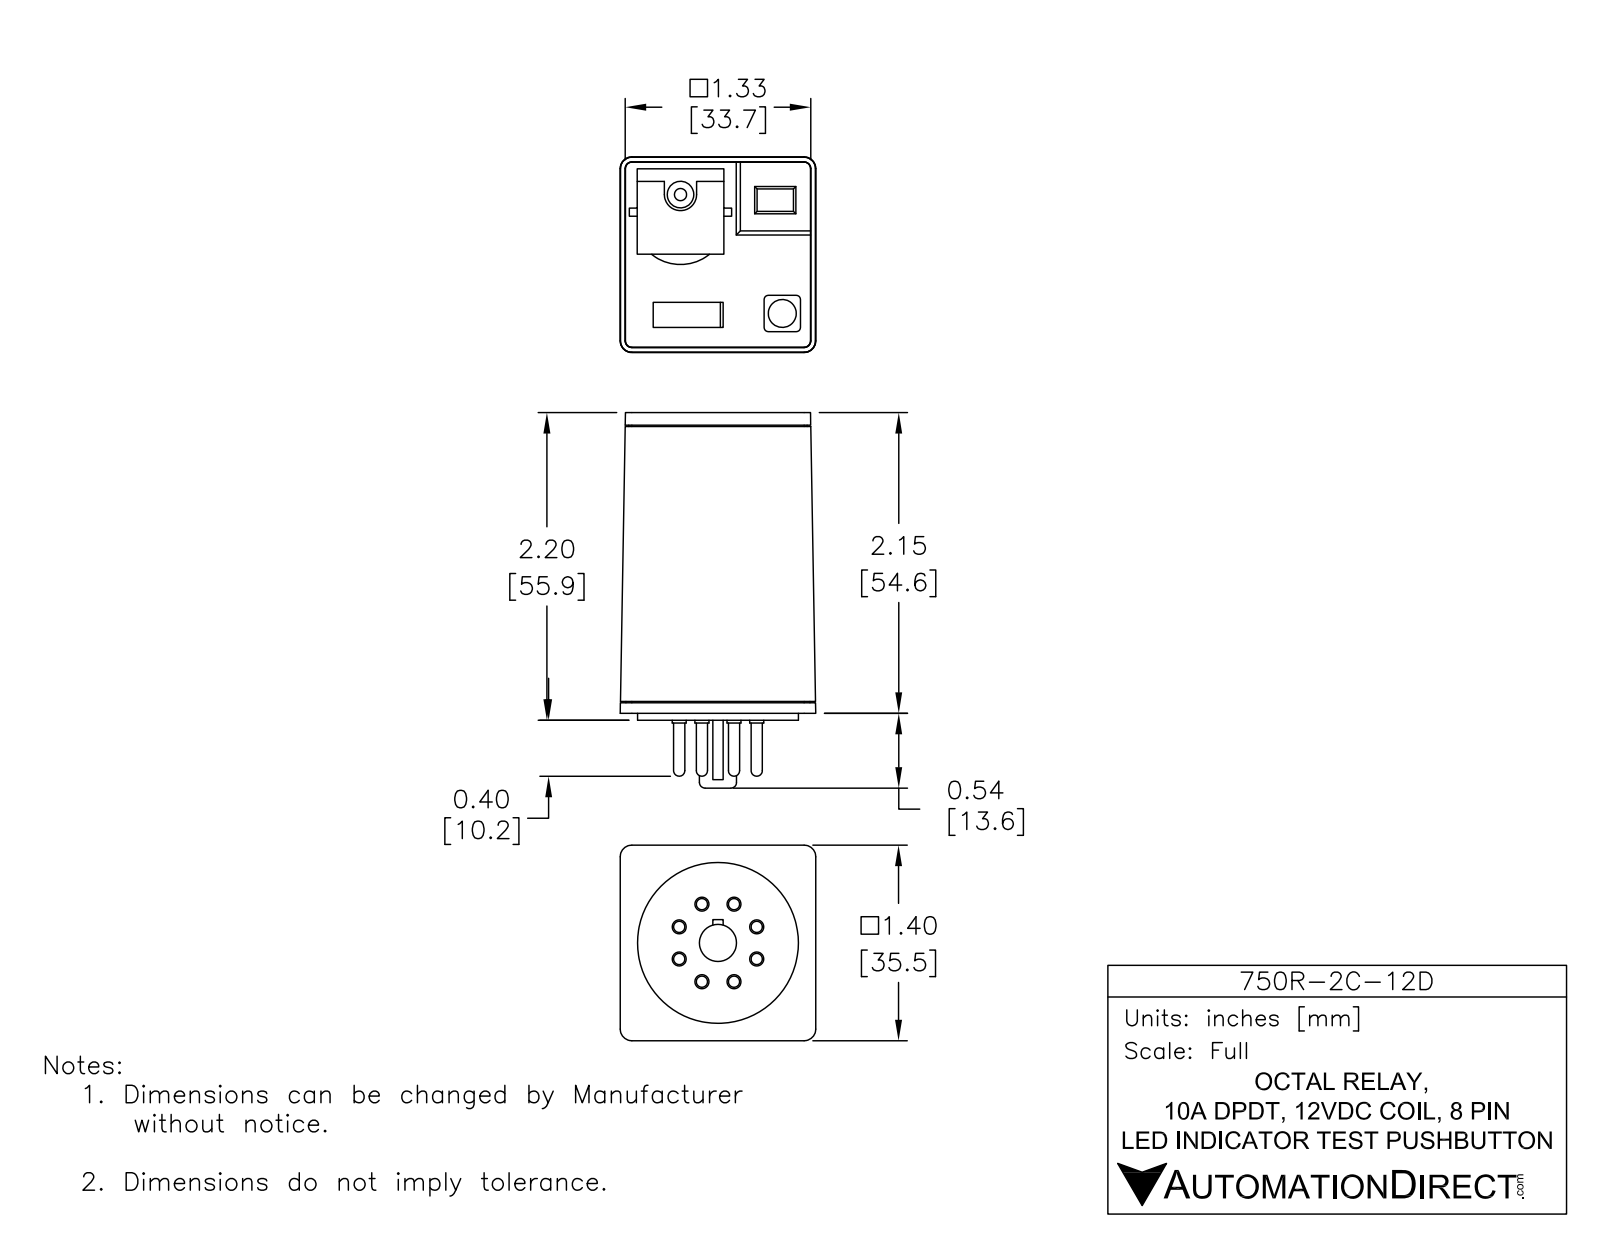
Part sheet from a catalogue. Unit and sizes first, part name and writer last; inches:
Units: inches
Overall size (bounding box): 2.685 × 1.398 × 1.398
Round holes (diameter × count): ⌀0.087 ×1, ⌀0.2 ×1
Round bosses / shafts (diameter × count): ⌀0.1 ×8, ⌀0.08 ×8, ⌀1.15 ×1, ⌀0.265 ×1, ⌀0.19 ×1
Partial cylindrical surfaces — rounded edges, fillets, slot ends (radius × count): R0.03 ×4, R0.115 ×1, R0.33 ×1
Main face-to-face distances: 0.05, 2.15, 2.2, 2.11, 0.04, 2.19, 2.14, 0.085, 0.03, 2.16
Hole centre spacings: 1.119
Volume: 4.047 in³ · Surface area: 17.37 in²
Bodies: 1 solid, 162 faces (90 planar, 50 cylindrical, 22 other)
Part name (STEP PRODUCT): 750R-2C-12D
STEP written by: SolidWorks 2014 (AUTOMOTIVE_DESIGN)
